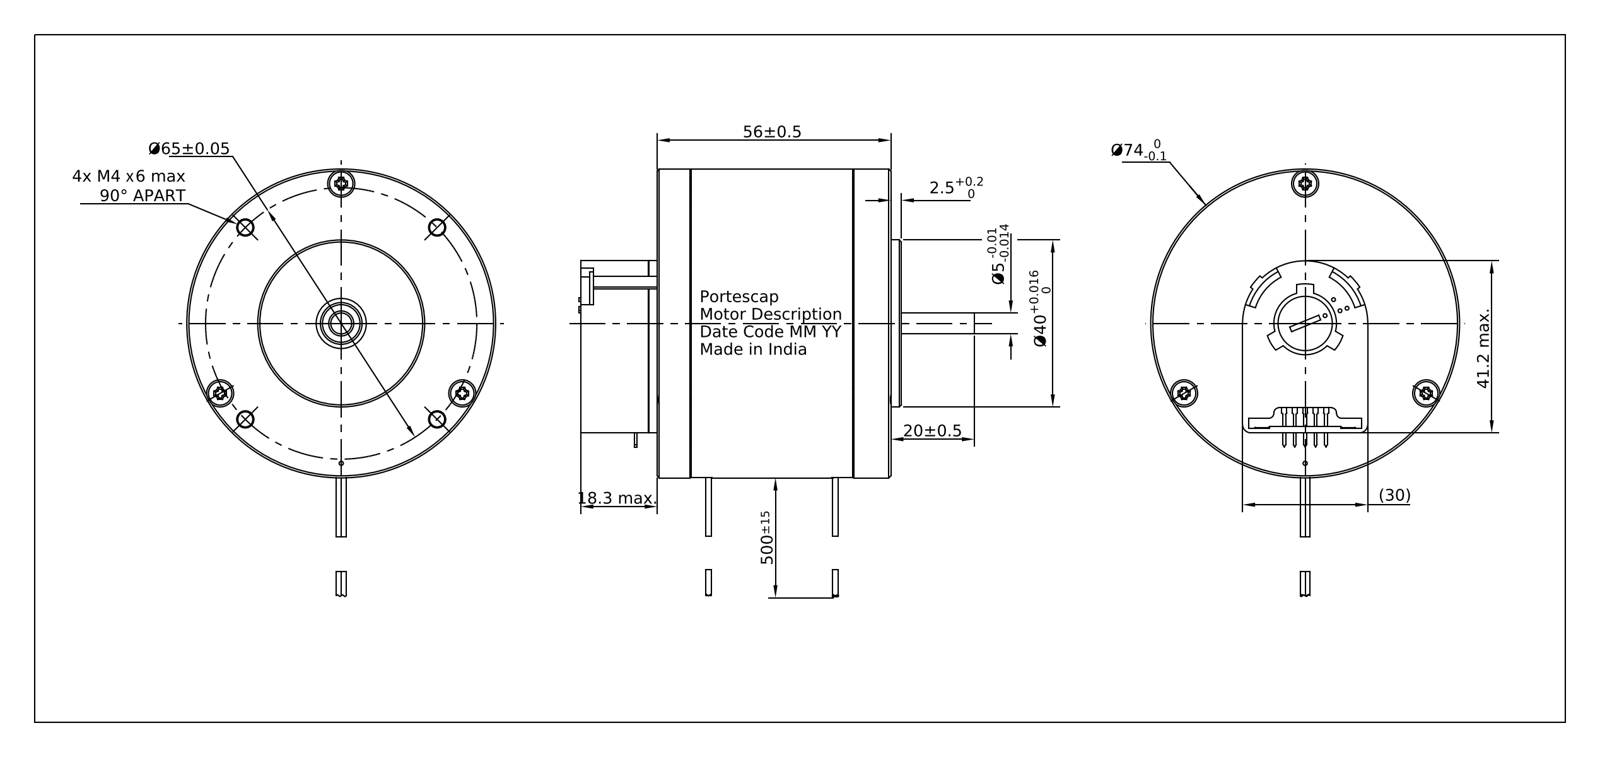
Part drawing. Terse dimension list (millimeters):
name: 7899896574; 7800906575_ASM; 7800906639_AF1; 7800906640_AF0 (+8 more)
written by: PRO/ENGINEER BY PARAMETRIC TECHNOLOGY CORPORATION, 2014310 (CONFIG_CONTROL_DESIGN)
unit: mm
bodies: 14 solids, 516 faces (292 planar, 159 cylindrical, 65 other)
size: 109.9 × 94.7 × 74
volume: 304 841 mm³; area: 50 837 mm²
holes: 4× ⌀3.6, 4× ⌀4, 3× ⌀1.6, 3× ⌀3, 3× ⌀3.2, 2× ⌀2.05, 2× ⌀2.44, 2× ⌀2.5, 1× ⌀11, 1× ⌀12
bosses: 4× ⌀1.25, 4× ⌀0.9, 3× ⌀2.5, 1× ⌀74, 1× ⌀70.6, 1× ⌀40, 1× ⌀13, 1× ⌀6
rounds: 4× R0.7, 4× R1.2, 2× R2, 1× R7.5, 1× R9.5, 1× R12.5, 1× R13.55, 1× R13.8
face distances: 39.2, 47.1, 7.9, 2.5, 3.5, 6.4, 45.6, 50, 53.5, 43.6
hole spacings: 26.63, 32.5, 39.77, 39.81, 45.96, 10.45, 18.1, 23.05
